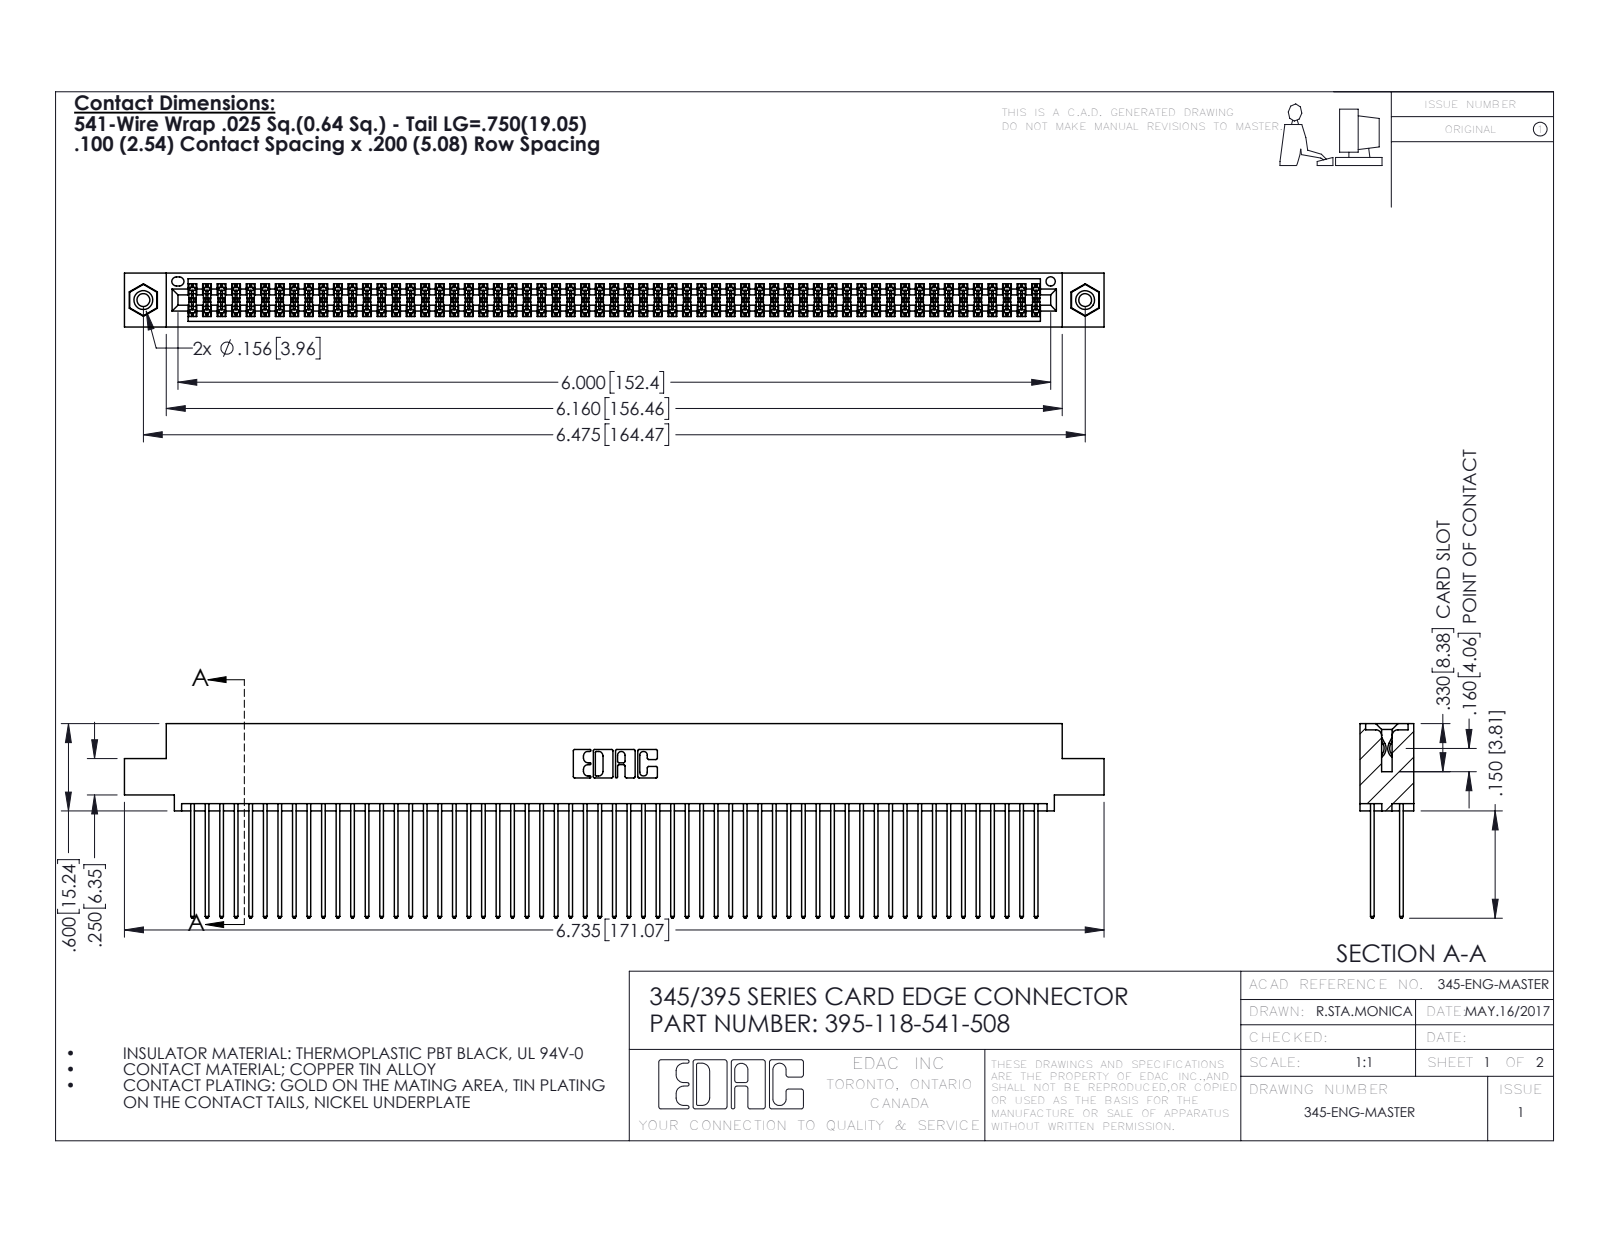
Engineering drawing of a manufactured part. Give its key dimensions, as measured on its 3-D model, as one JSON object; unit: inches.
{"part_name": "395-118-541-508; 345-250-001_345-250-003-102; 345 Part_0.110 Offset - 0.156 Dia-TI; 345-292-001_345-293-141", "step_written_by": "SolidWorks 2016 (CONFIG_CONTROL_DESIGN)", "units": "inches", "bodies": {"solids": 121, "faces": 6090, "planar": 4010, "cylindrical": 2064, "other": 16}, "overall_size": [6.735, 1.337, 0.37], "volume_in3": 1.06, "surface_area_in2": 45.41, "round_holes": [[0.089, 2], [0.125, 2], [0.156, 2], [0.064, 1]], "round_bosses_or_shafts": [[0.155, 2]], "partial_cylinders_radius": [[0.006, 177], [0.01, 118], [0.01, 22], [0.007, 6], [0.031, 6], [0.026, 3], [0.014, 2], [0.019, 2]], "face_to_face_distances": [0.072, 0.298, 0.2, 0.098, 0.272, 0.025, 0.225, 0.37, 0.175, 0.149], "hole_center_spacings": [0.27, 6.239, 6.475]}
